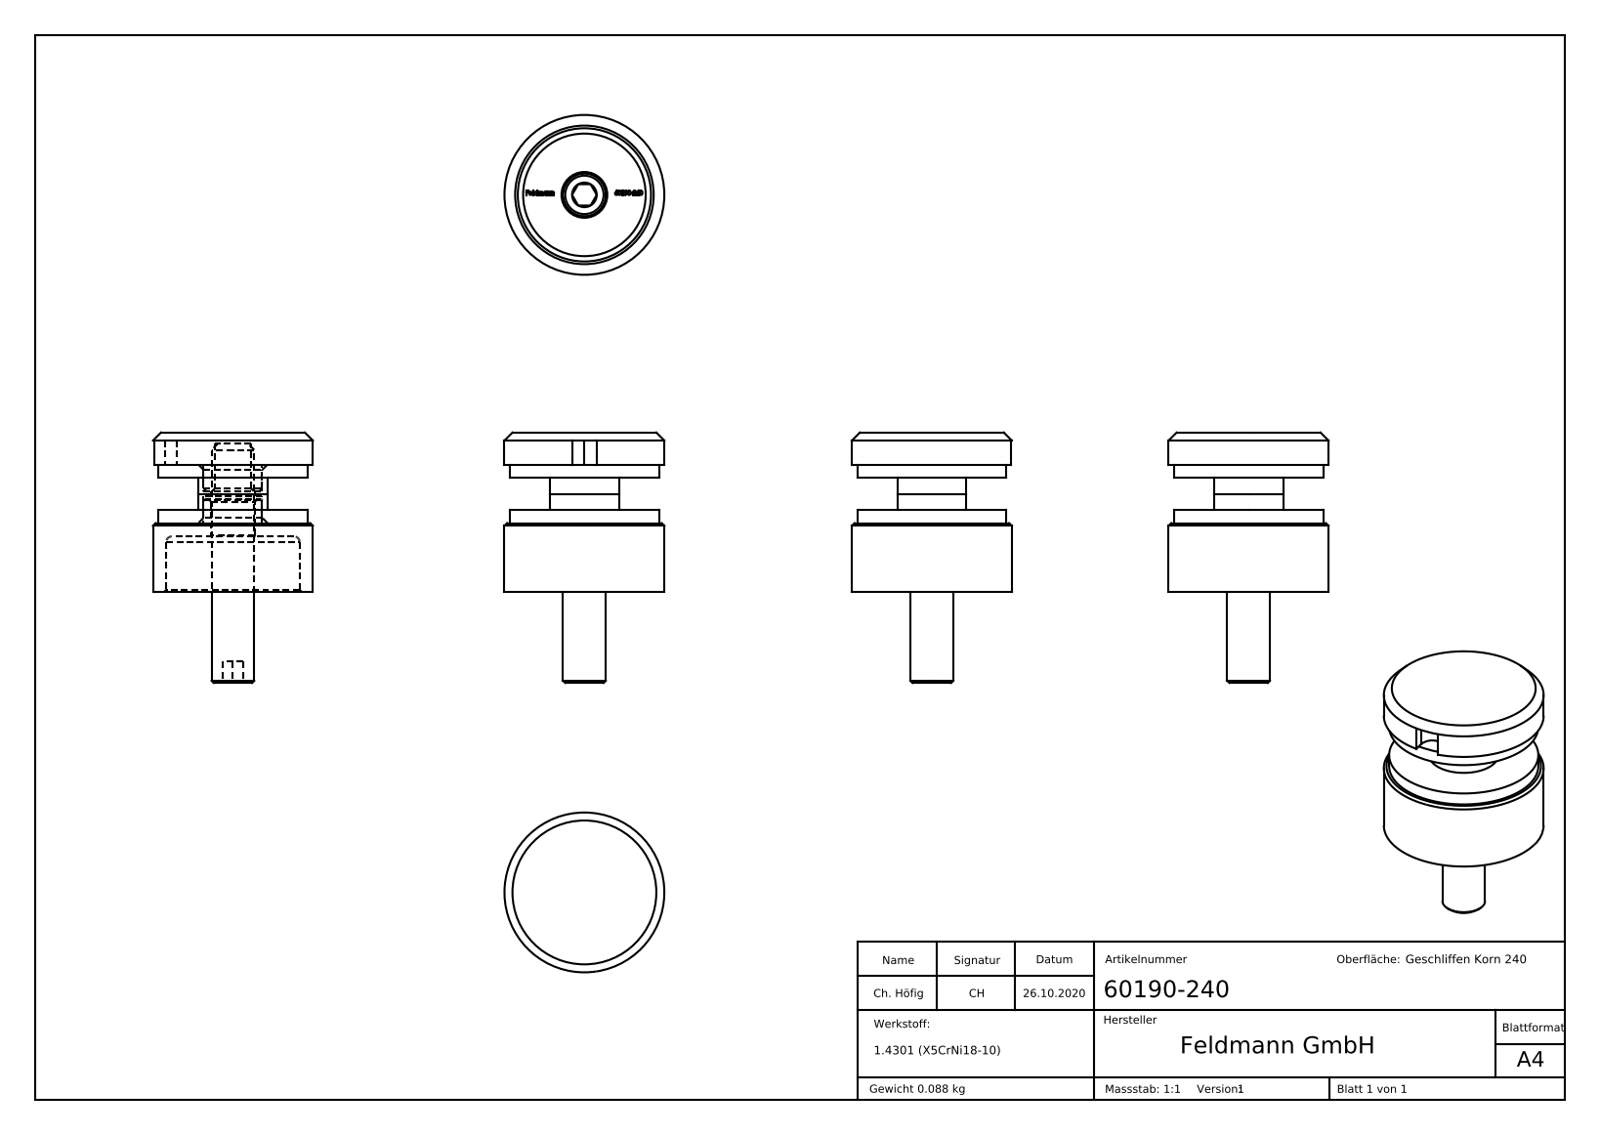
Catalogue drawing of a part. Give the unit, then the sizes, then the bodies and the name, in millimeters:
Units: millimetres
Overall size (bounding box): 47 × 30 × 30
Round holes (diameter × count): ⌀6.8 ×1, ⌀8.2 ×1, ⌀11 ×1, ⌀25 ×1
Round bosses / shafts (diameter × count): ⌀30 ×1, ⌀28 ×1, ⌀13 ×1, ⌀8 ×1
Partial cylindrical surfaces — rounded edges, fillets, slot ends (radius × count): R2.25 ×1
Main face-to-face distances: 11, 2.4, 8.6, 6, 17, 8.4, 6.2, 14.6, 2.5, 4.9
Volume: 13 209 mm³ · Surface area: 10 394 mm²
Bodies: 5 solids, 304 faces (143 planar, 34 cylindrical, 127 other)
Part name (STEP PRODUCT): 6019X-240 Teil3; 6019X-240 Teil3_6019X-240 Teil3; 60190-240 Teil1_6019X-240 Teil1; 60190-240 (+5 more)
STEP written by: SolidWorks 2018 (CONFIG_CONTROL_DESIGN)
